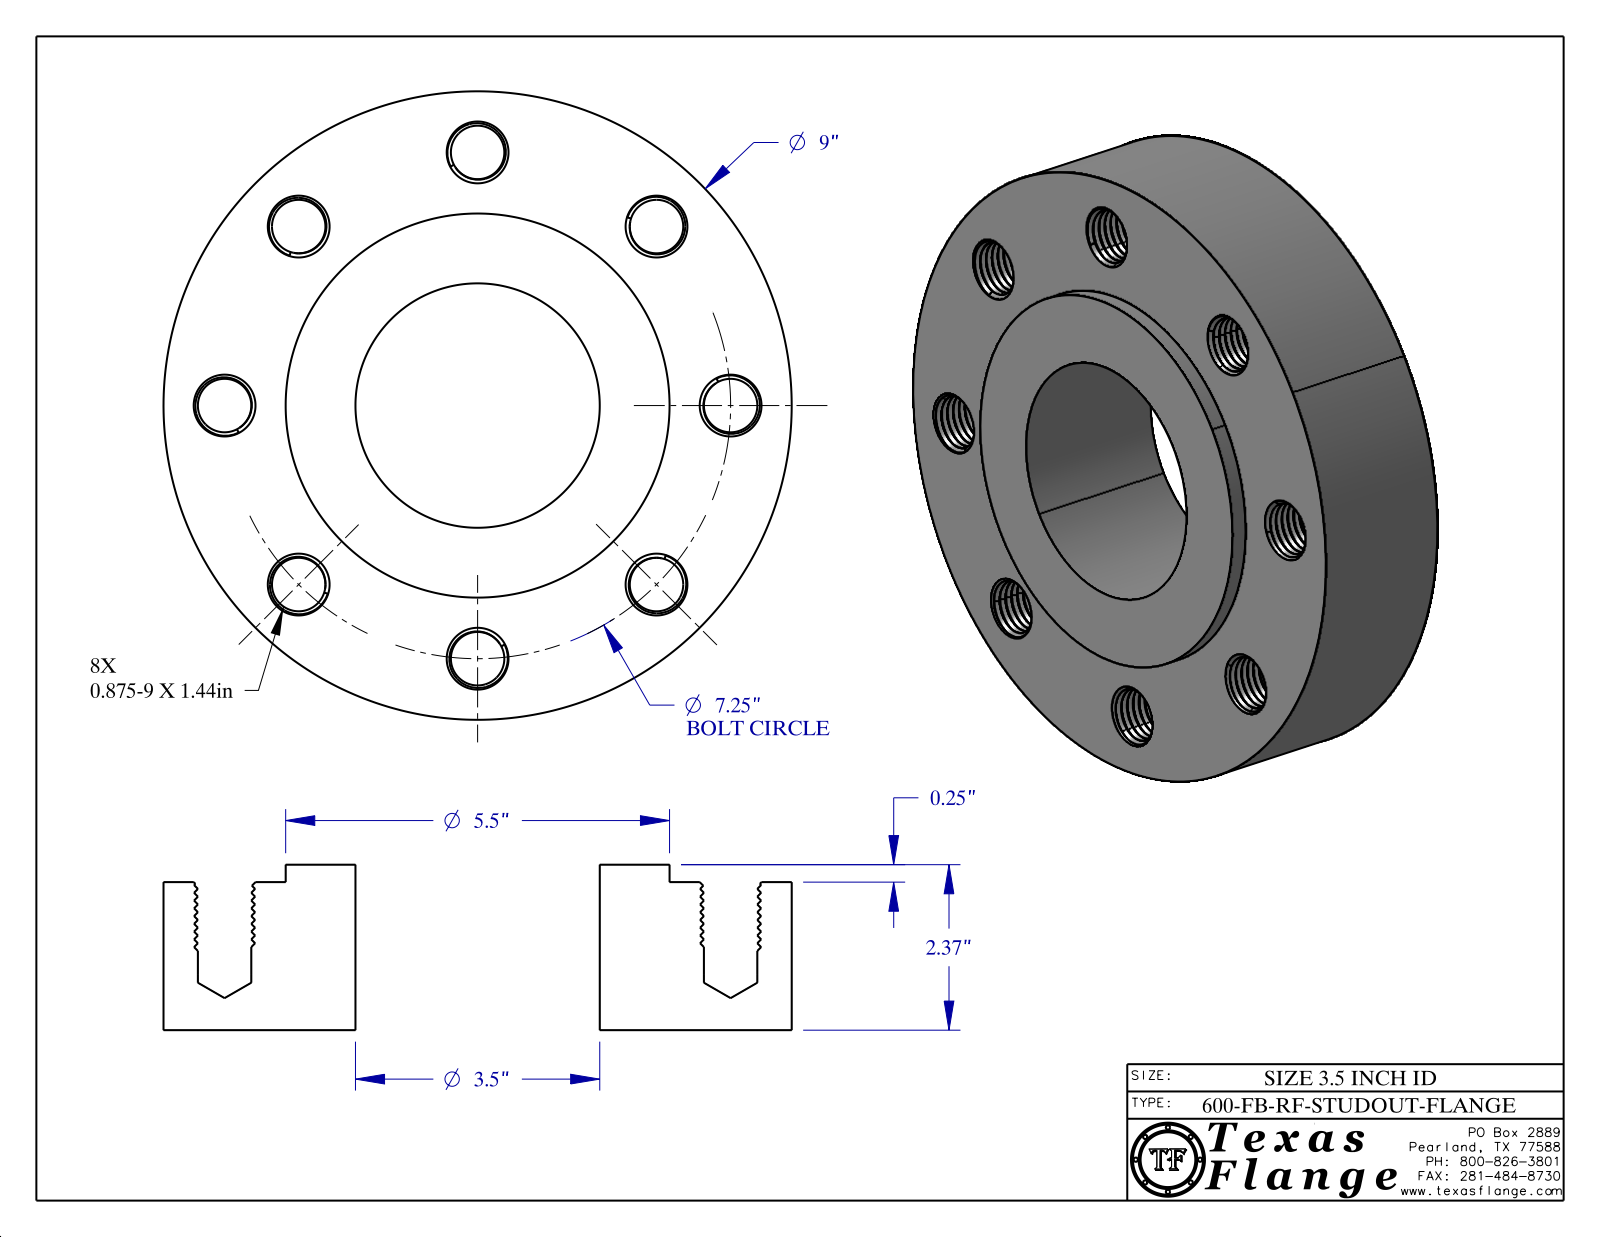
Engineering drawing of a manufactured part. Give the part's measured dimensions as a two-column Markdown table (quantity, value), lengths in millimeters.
| quantity | value |
| --- | --- |
| part name | 3.5-600-FB-RF-STUDOUT-FLANGE |
| STEP written by | CATIA V5 STEP AP214 (AUTOMOTIVE_DESIGN) |
| units | millimeters |
| bodies | 1 solid, 874 faces (368 planar, 186 cylindrical, 320 other) |
| overall size | 228.6 × 228.6 × 60.2 |
| volume | 1 834 000 mm³ |
| surface area | 151 500 mm² |
| round holes (diameter × count) | 19.5 × 8, 25.4 × 1, 88.9 × 1 |
| round bosses / shafts (diameter × count) | 1.5 × 8, 228.6 × 1, 139.7 × 1, 20 × 1 |
| main face-to-face distances | 53.8, 6.4, 60.2, 0.4, 59.8, 53.5, 7.6, 7.4, 1.4, 6.3 |
| hole center spacings | 70.5, 92.1, 130.2, 170.1, 184.2 |
